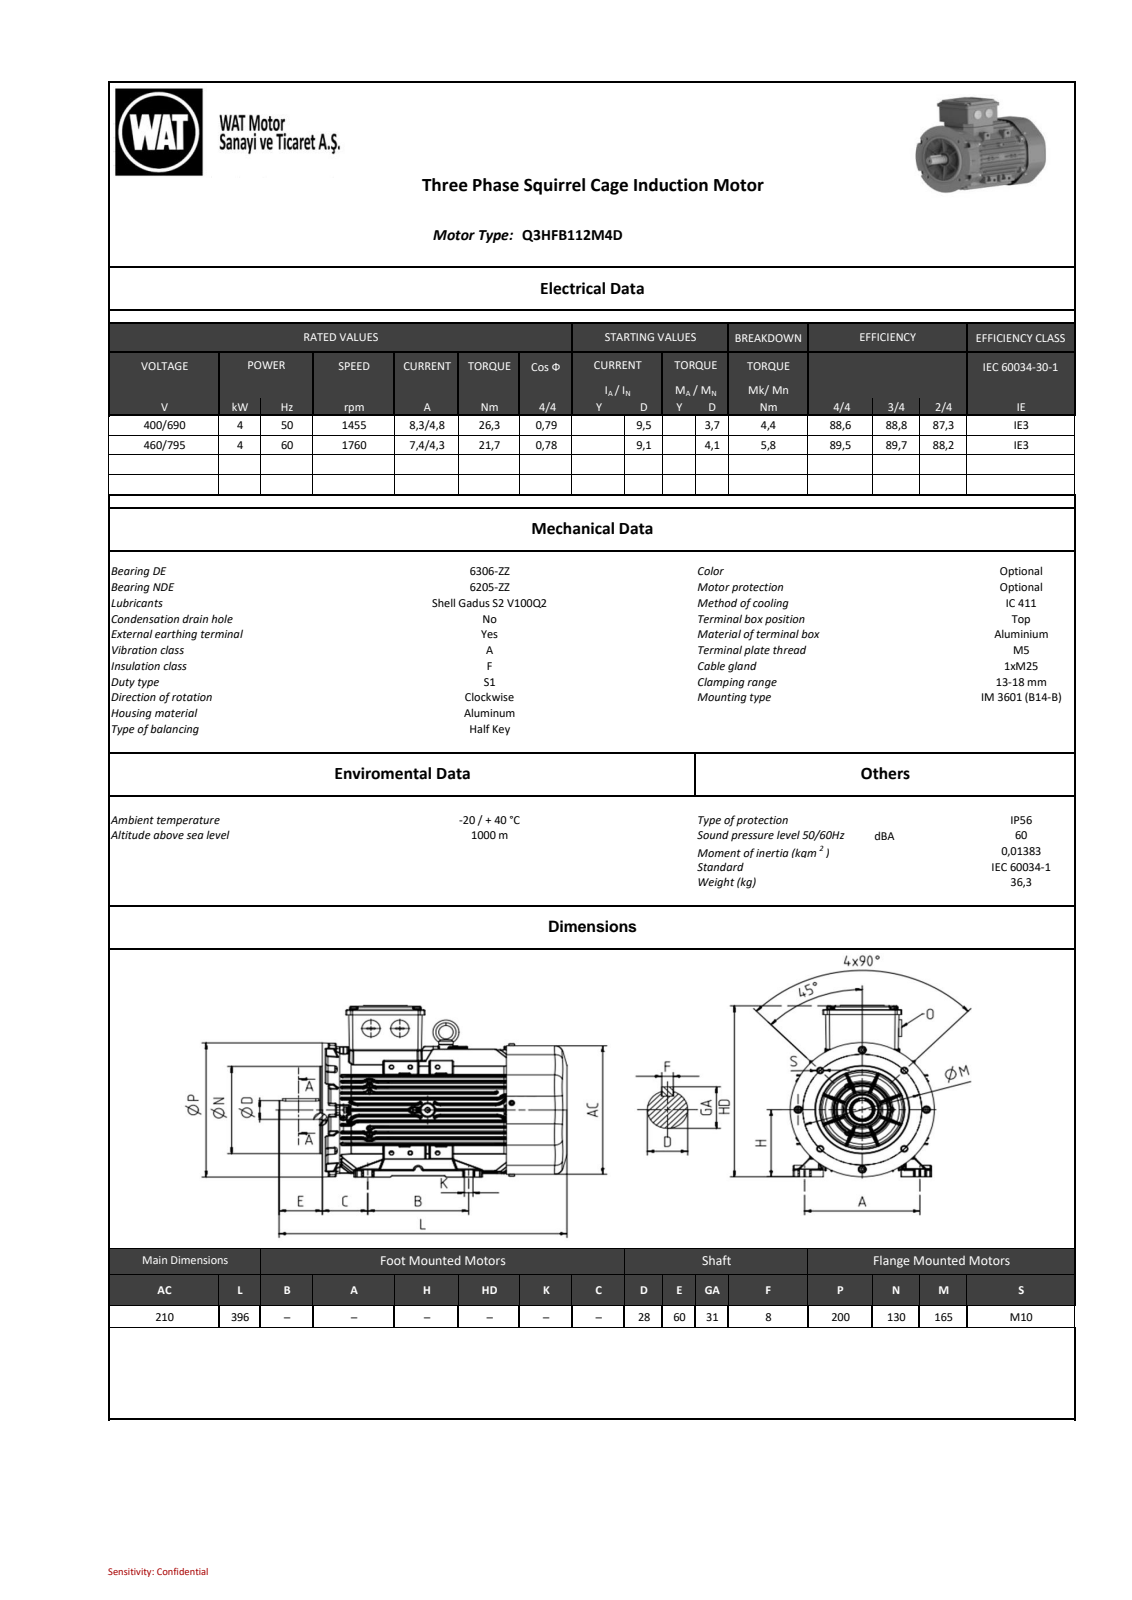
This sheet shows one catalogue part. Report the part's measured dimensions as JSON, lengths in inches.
{"part_name": "QH series_ 112_B14b_stp_objects", "step_written_by": "SIEMENS PLM Software NX2206.8101 (AUTOMOTIVE_DESIGN)", "units": "inches", "bodies": {"solids": 0, "faces": 6155, "planar": 1394, "cylindrical": 2344, "other": 2417}, "overall_size": [15.591, 10.531, 8.622], "round_holes": [[0.181, 2], [0.315, 1], [0.335, 1]], "round_bosses_or_shafts": [[0.394, 4], [0.315, 4], [0.984, 2], [0.236, 2], [7.402, 1], [5.118, 1], [1.411, 1], [1.181, 1]], "partial_cylinders_radius": [[0.031, 576], [0.079, 526], [0.02, 380], [0.039, 155], [0.118, 60], [0.157, 10], [0.098, 8], [0.02, 6]], "face_to_face_distances": [0.039, 0.433, 0.846, 1.416, 3.919, 0.983, 3.56, 2.714, 0.321, 4.444]}
